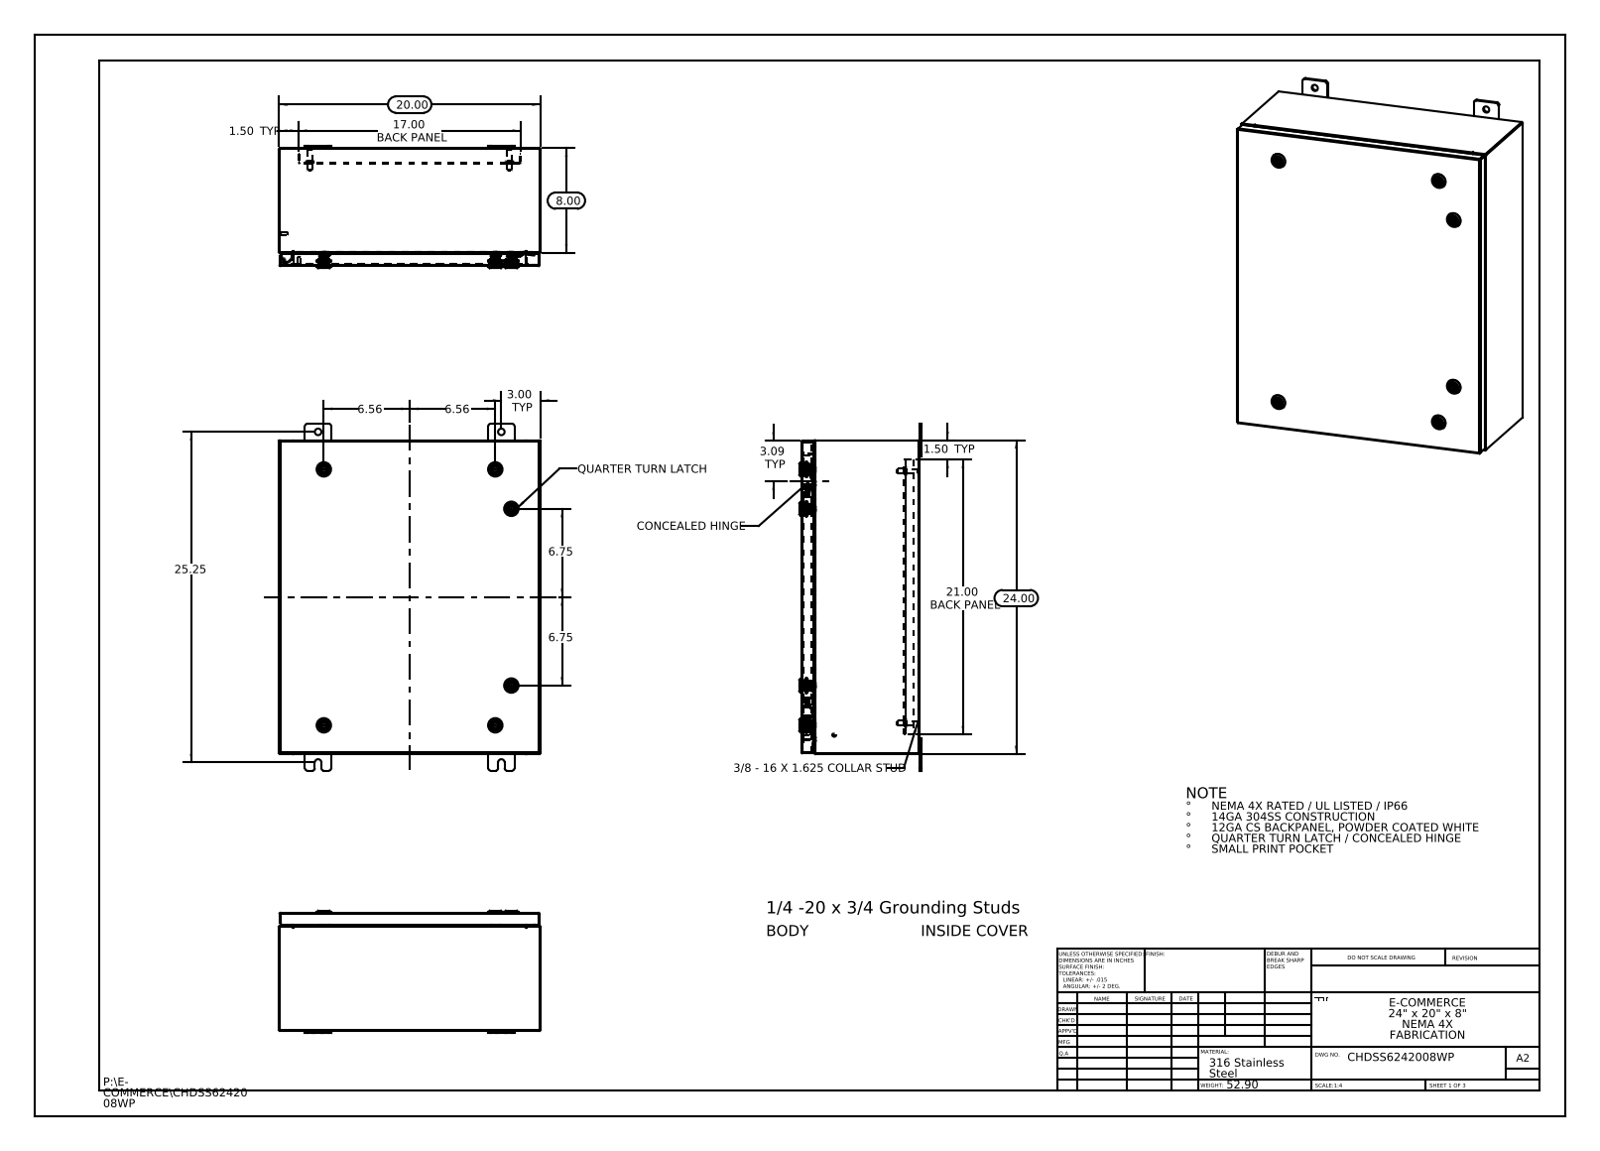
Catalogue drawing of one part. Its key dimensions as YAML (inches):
part_name: "CHDSS6242008WP; HW-CLH-R001-0500_2412-026240-2445-Industrilas; Concealed Hinge enclosure side; Concealed Hinge (Cover Side) (+8 more)"
step_written_by: "SolidWorks 2013 (CONFIG_CONTROL_DESIGN)"
units: inches
bodies: {solids: 55, faces: 5420, planar: 1592, cylindrical: 1692, other: 2136}
overall_size: [26.5, 20, 9.356]
volume: 189.1
surface_area: 4727
round_holes:
  - {diameter: 0.5, count: 8}
  - {diameter: 0.197, count: 6}
  - {diameter: 0.394, count: 6}
  - {diameter: 0.4, count: 6}
  - {diameter: 0.63, count: 6}
  - {diameter: 0.787, count: 6}
  - {diameter: 0.136, count: 4}
  - {diameter: 0.211, count: 1}
round_bosses_or_shafts:
  - {diameter: 0.236, count: 8}
  - {diameter: 1.102, count: 6}
  - {diameter: 0.78, count: 6}
  - {diameter: 0.626, count: 6}
  - {diameter: 0.61, count: 6}
  - {diameter: 0.531, count: 6}
  - {diameter: 0.392, count: 6}
  - {diameter: 0.114, count: 6}
partial_cylinders:
  - {radius: 0.118, count: 198}
  - {radius: 0.006, count: 196}
  - {radius: 0.028, count: 72}
  - {radius: 0.02, count: 24}
  - {radius: 0.19, count: 24}
  - {radius: 0.197, count: 24}
  - {radius: 0.013, count: 20}
  - {radius: 0.088, count: 18}
face_to_face_distances: [0.075, 0.074, 9.01, 8.935, 8.936, 8.861, 0.104, 19.925, 1, 1.075]
hole_center_spacings: [0.688, 1.858, 2.878, 3.065, 13.1, 14, 14.164, 14.187]
